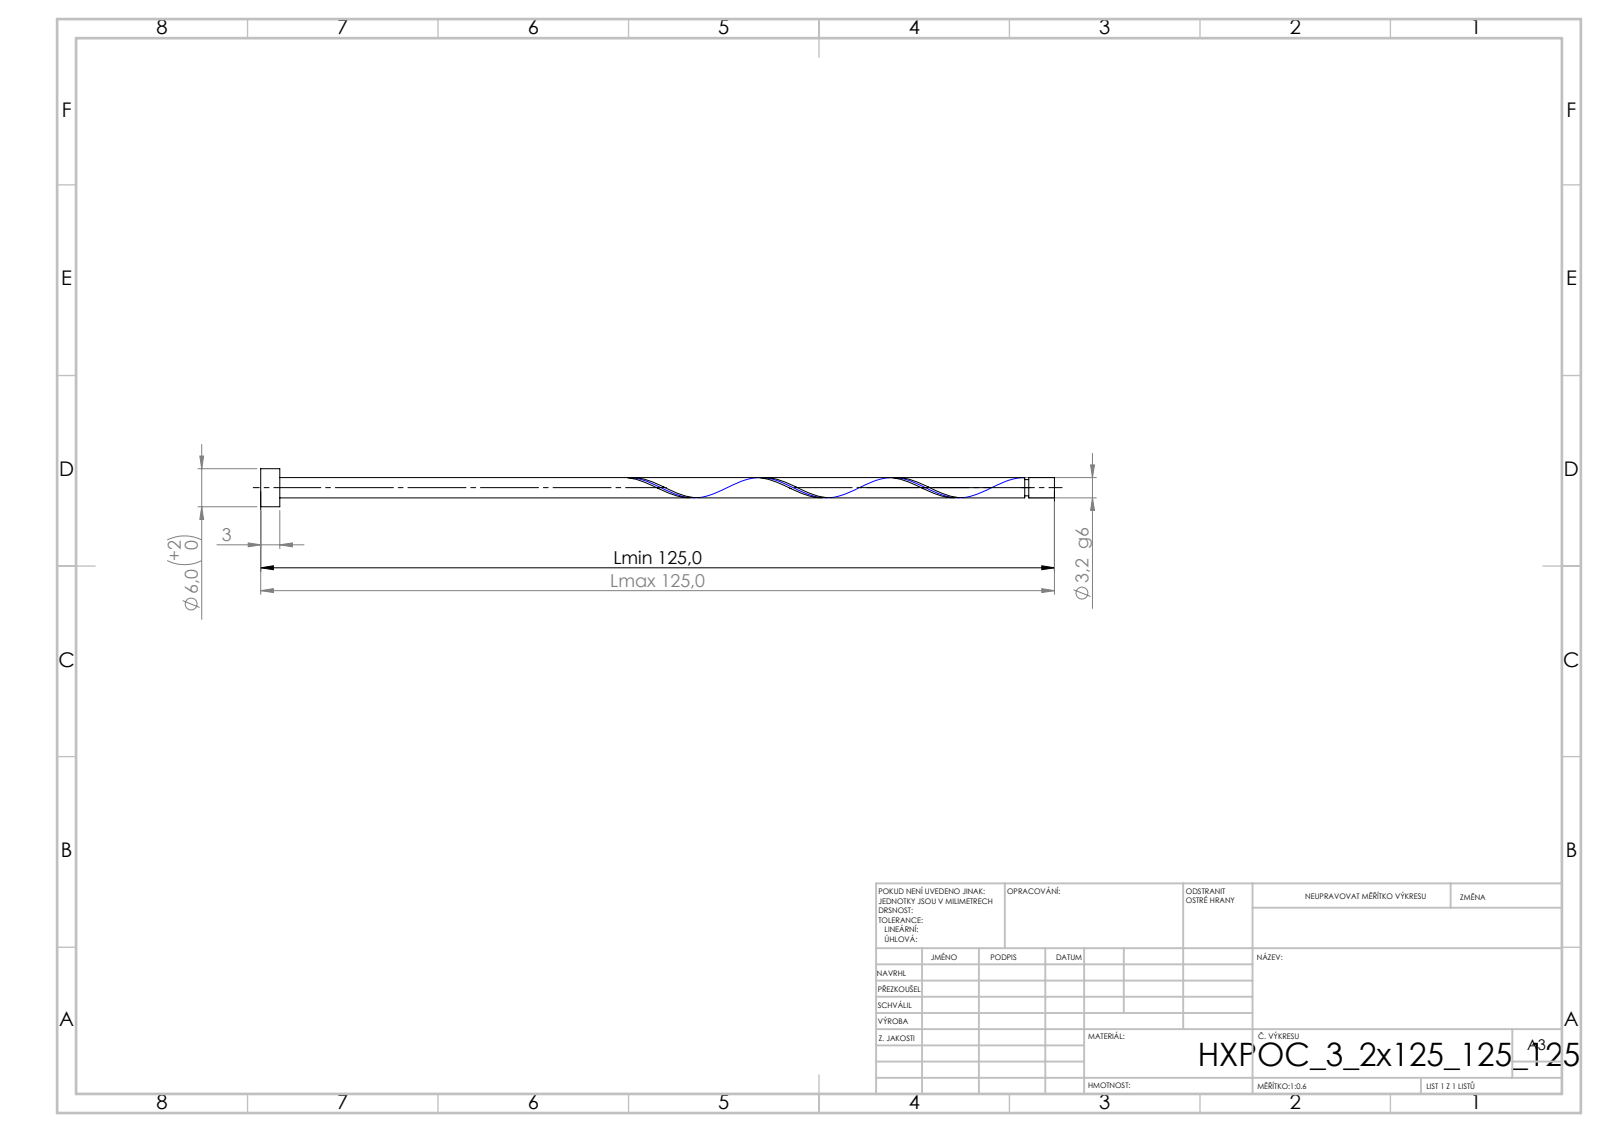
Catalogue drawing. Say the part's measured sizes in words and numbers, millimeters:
Its 3-D file was written by "SolidWorks 2019 (CONFIG_CONTROL_DESIGN)". It is 1 solid with 21 faces: 6 planar, 14 cylindrical and 1 other. Overall it measures 125 by 6 by 6 millimeters. Its volume is 1 055 cubic millimeters and its surface area 1 366 square millimeters. Round bosses or shafts: 1 of diameter 6, 1 of diameter 3.2, 1 of diameter 2.56. The main face-to-face distances are 3, 125, 122, 120.96, 117.96, 4.04, 120.32, 117.32, 0.64, 4.68.
